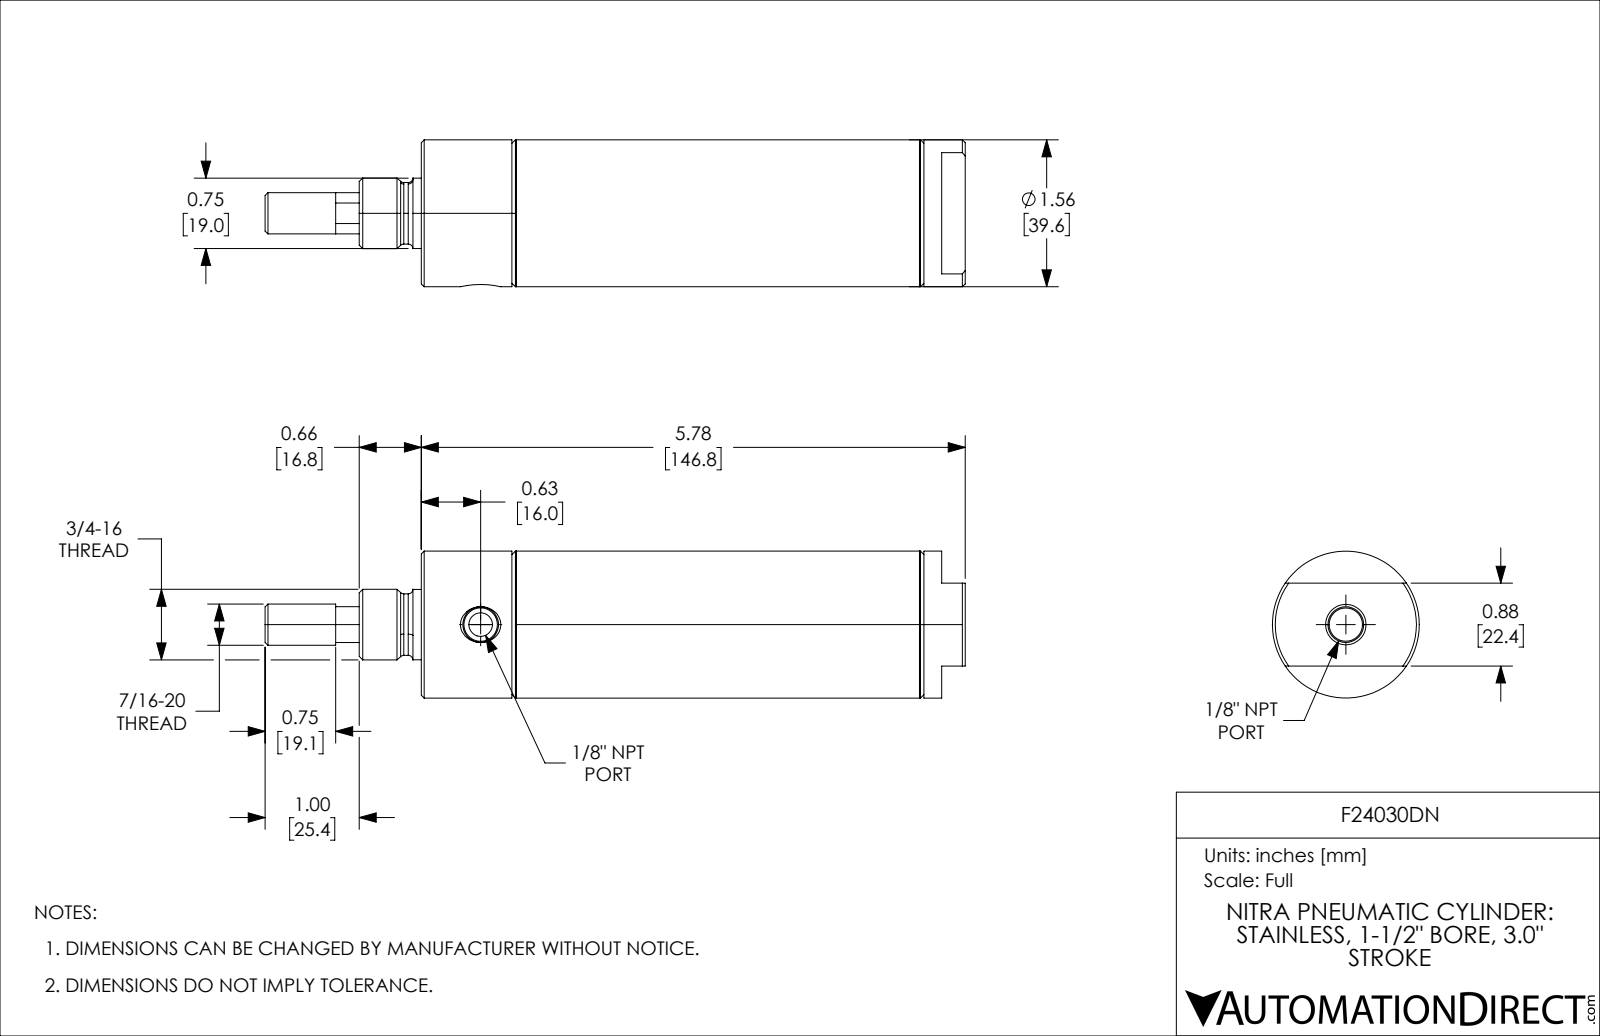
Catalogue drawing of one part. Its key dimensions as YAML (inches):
part_name: "F24030DN_3; F24030DN_5; F24030DN_7; F24030DN_9 (+1 more)"
step_written_by: "SolidWorks 2021 (CONFIG_CONTROL_DESIGN)"
units: inches
bodies: {solids: 4, faces: 126, planar: 28, cylindrical: 42, other: 56}
overall_size: [7.438, 1.56, 1.56]
volume: 6.05
surface_area: 81.89
round_holes:
  - {diameter: 0.25, count: 1}
  - {diameter: 0.462, count: 1}
  - {diameter: 0.973, count: 1}
  - {diameter: 1.431, count: 1}
round_bosses_or_shafts:
  - {diameter: 1.56, count: 1}
  - {diameter: 1.511, count: 1}
  - {diameter: 0.75, count: 1}
  - {diameter: 0.748, count: 1}
  - {diameter: 0.654, count: 1}
  - {diameter: 0.438, count: 1}
  - {diameter: 0.437, count: 1}
face_to_face_distances: [0.875, 0.25, 0.438, 3, 3.875, 1.215, 4.215, 5.09, 5.778, 4.563]
